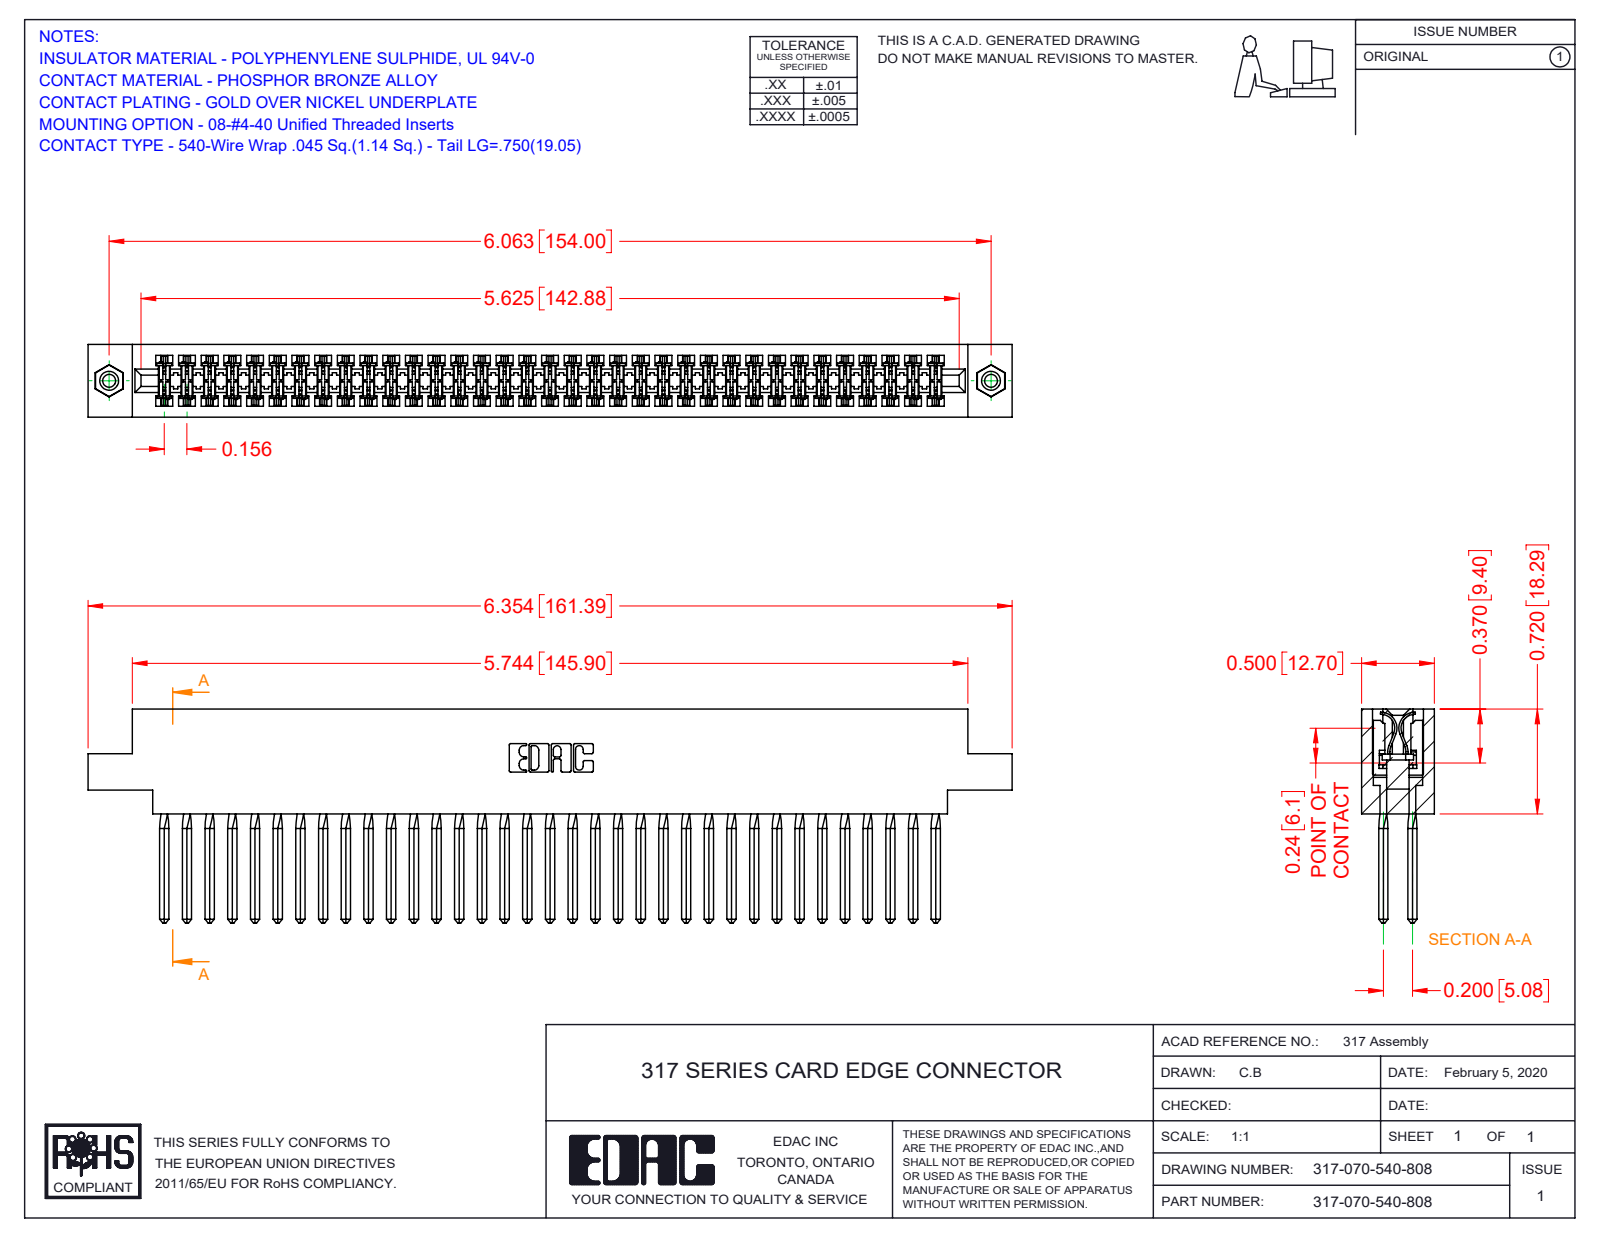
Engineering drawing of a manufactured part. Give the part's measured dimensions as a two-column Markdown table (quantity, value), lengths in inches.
| quantity | value |
| --- | --- |
| part name | 317-070-540-878; 345-250-001_345-250-003-102; 317 Part_.156 Dia - TI; 317-290-001_540 |
| STEP written by | SolidWorks 2016 (CONFIG_CONTROL_DESIGN) |
| units | inches |
| bodies | 73 solids, 6392 faces (5200 planar, 896 cylindrical, 296 other) |
| overall size | 6.354 × 1.47 × 0.5 |
| volume | 1.638 in³ |
| surface area | 61.66 in² |
| round holes (diameter × count) | 0.089 × 2, 0.125 × 2, 0.156 × 2 |
| round bosses / shafts (diameter × count) | 0.155 × 2 |
| partial cylindrical surfaces (radius × count) | 0.015 × 140, 0.01 × 22, 0.007 × 6, 0.031 × 6, 0.026 × 3, 0.095 × 2, 0.1 × 2, 0.11 × 2 |
| main face-to-face distances | 0.5, 0.075, 0.425, 0.35, 0.195, 0.11, 0.094, 0.2, 0.115, 0.131 |
| hole center spacings | 6.063 |
